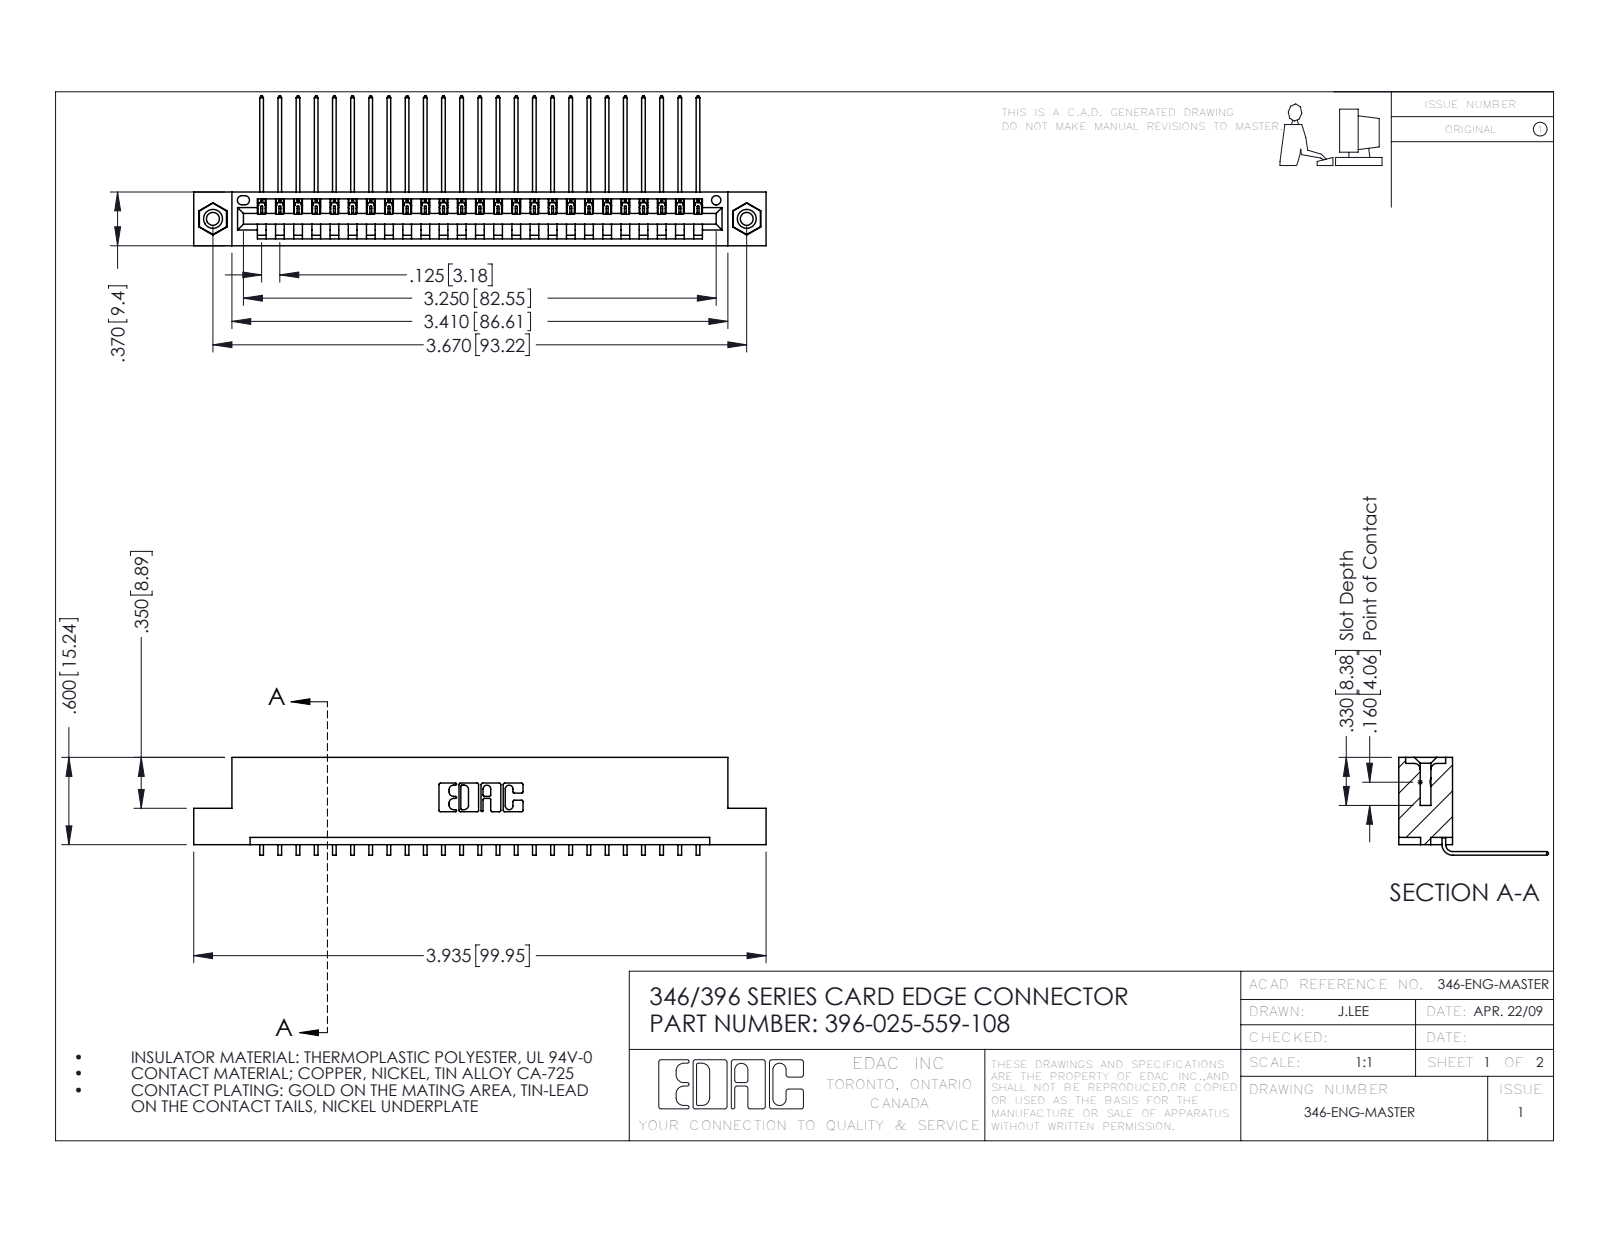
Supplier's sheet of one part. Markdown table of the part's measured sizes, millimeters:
| quantity | value |
| --- | --- |
| part name | 345-292-001_558 559 Tail - 1; 346 Part_Flush Mounting Lugs - 0.156 Dia-TI; 345-250-001_345-250-003-102; 396-025-559-108 |
| STEP written by | SolidWorks 2016 (CONFIG_CONTROL_DESIGN) |
| units | millimeters |
| bodies | 28 solids, 1682 faces (1158 planar, 508 cylindrical, 16 other) |
| overall size | 99.9 × 26.2 × 17.1 |
| volume | 9 520 mm³ |
| surface area | 12 250 mm² |
| round holes (diameter × count) | 2.3 × 2, 3.2 × 2, 4 × 2, 1.6 × 1 |
| round bosses / shafts (diameter × count) | 3.9 × 2 |
| partial cylindrical surfaces (radius × count) | 0.2 × 50, 0.3 × 22, 0.2 × 6, 0.8 × 6, 0.7 × 3, 0.8 × 2, 1 × 2, 0.4 × 1 |
| main face-to-face distances | 1.2, 8.2, 9.4, 6.4, 1.8, 0.6, 7.6, 3.8, 5.6, 2.5 |
| hole center spacings | 6.2, 87.9, 93.2 |
